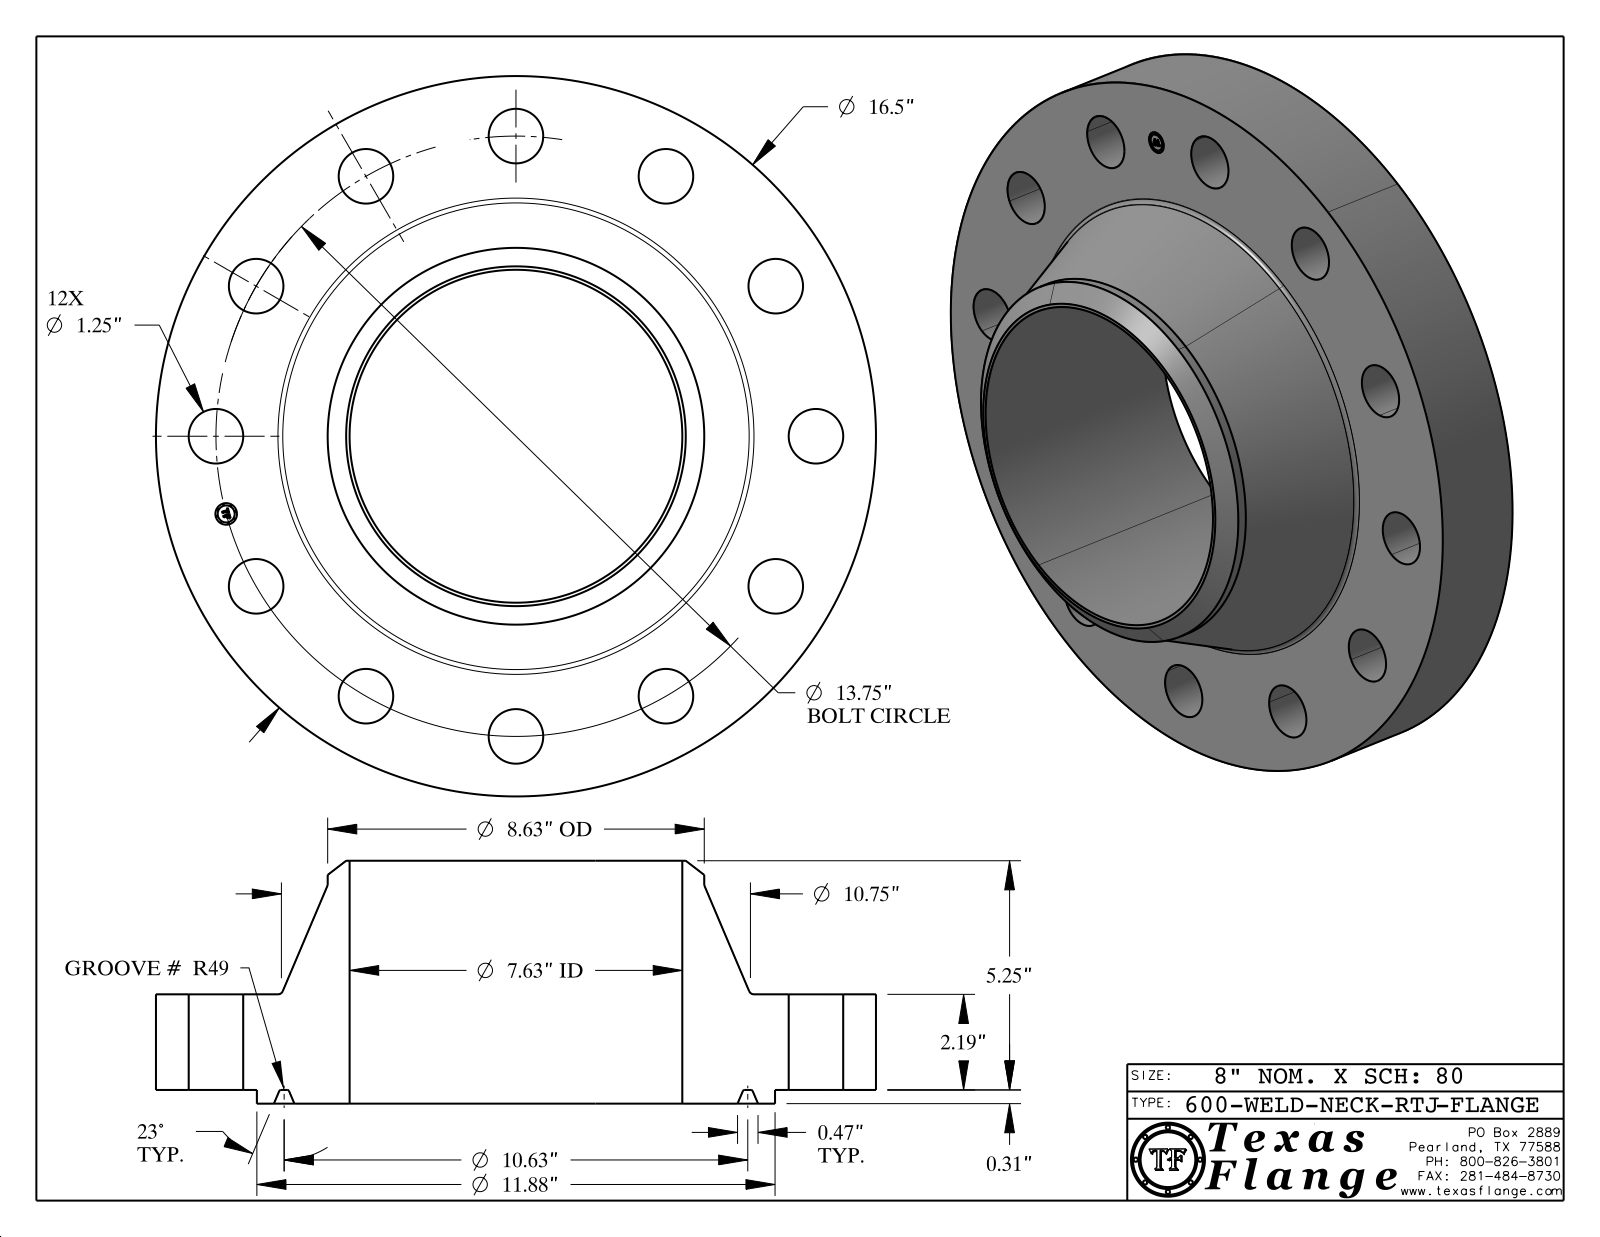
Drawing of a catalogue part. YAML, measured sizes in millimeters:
part_name: "600-WELD-NECK-RTJ"
step_written_by: "CATIA V5 STEP AP214 (AUTOMOTIVE_DESIGN)"
units: millimeters
bodies: {solids: 1, faces: 437, planar: 371, cylindrical: 52, other: 14}
overall_size: [419.1, 419.1, 141.3]
volume: 7033000
surface_area: 478100
round_holes:
  - {diameter: 31.8, count: 12}
  - {diameter: 12.6, count: 1}
  - {diameter: 193.7, count: 1}
round_bosses_or_shafts:
  - {diameter: 0.8, count: 8}
  - {diameter: 419.1, count: 1}
  - {diameter: 301.6, count: 1}
  - {diameter: 219.2, count: 1}
  - {diameter: 9.9, count: 1}
face_to_face_distances: [55.6, 8, 63.6, 141.3, 133.4, 77.7, 63.2, 55.2, 0.4, 78.1]
hole_center_spacings: [174.6, 174.6, 247, 302.5, 337.3, 90.4, 90.4, 349.3]
